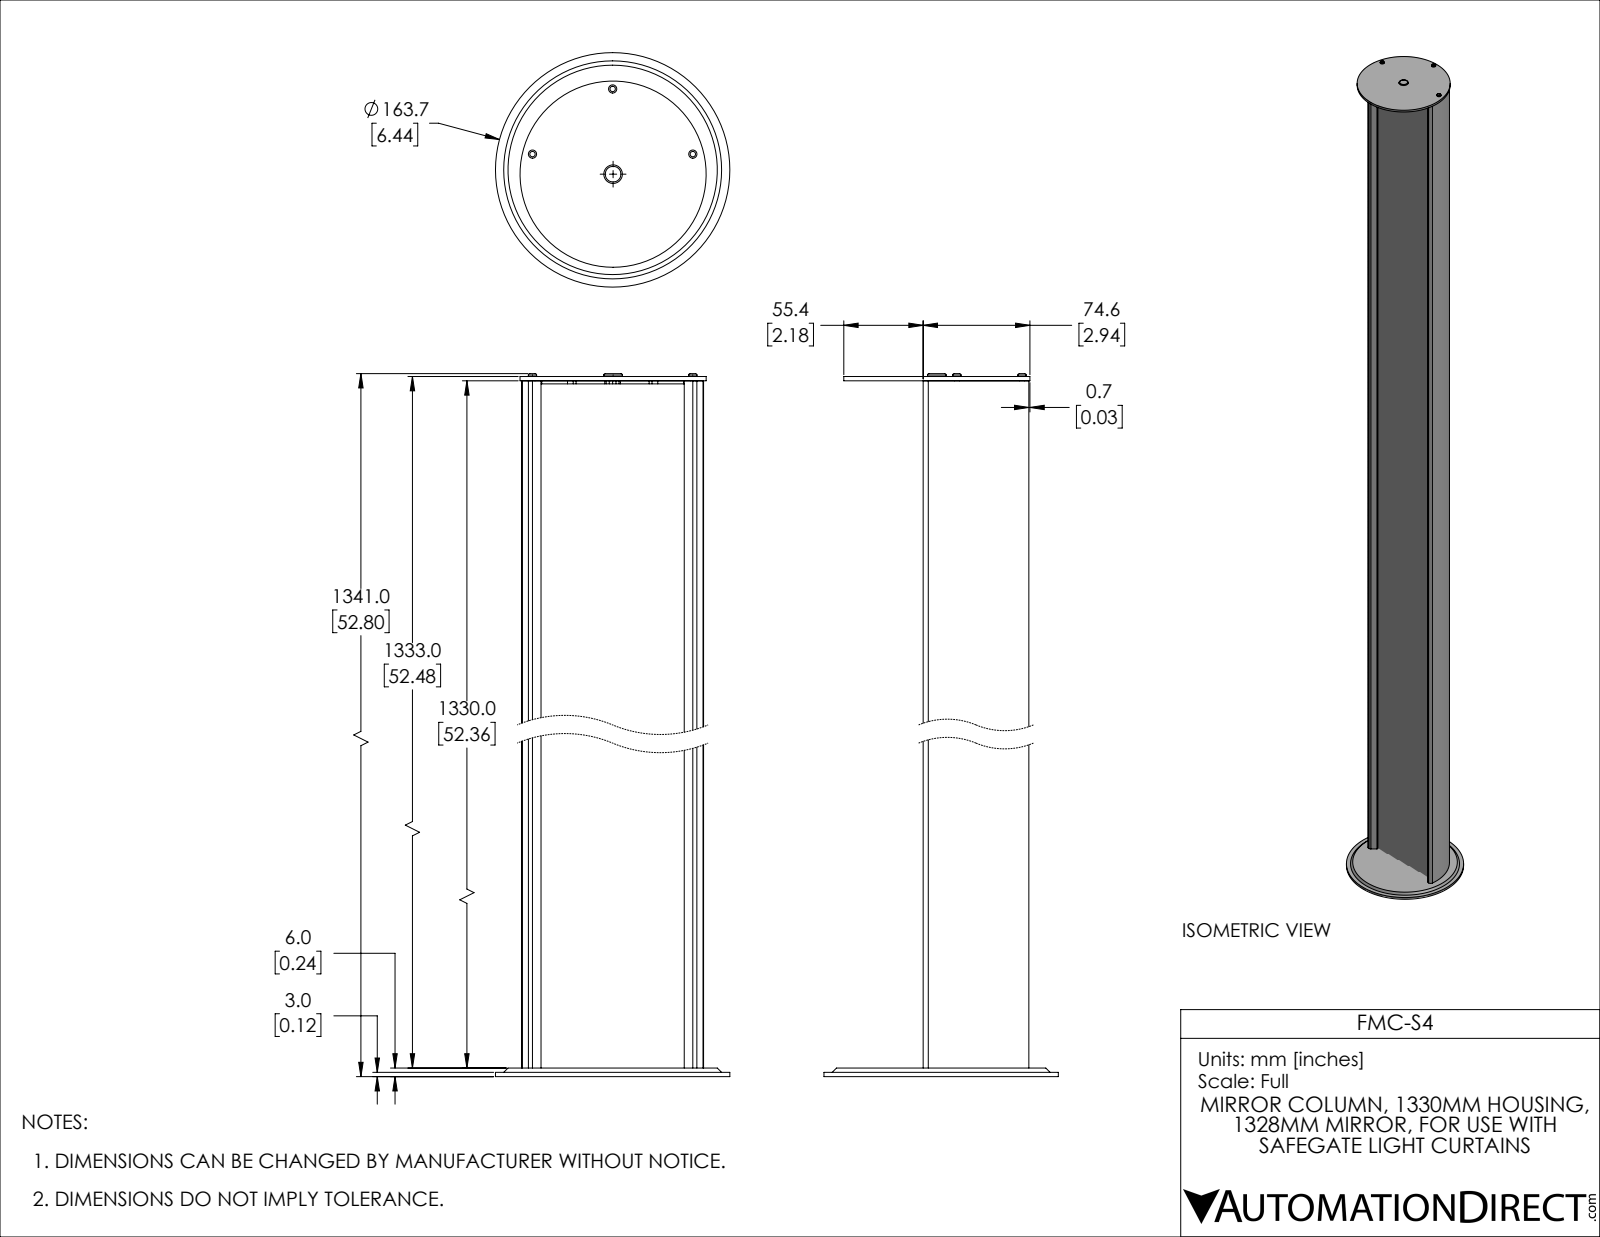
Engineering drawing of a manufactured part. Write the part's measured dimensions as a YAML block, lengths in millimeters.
part_name: "FMC-S4"
step_written_by: "SolidWorks 2019 (AUTOMOTIVE_DESIGN)"
units: millimeters
bodies: {solids: 11, faces: 192, planar: 82, cylindrical: 102, other: 8}
overall_size: [1341, 163.7, 163.7]
volume: 2411000
surface_area: 1668000
round_holes:
  - {diameter: 4, count: 3}
  - {diameter: 8.5, count: 3}
  - {diameter: 30, count: 1}
round_bosses_or_shafts:
  - {diameter: 6.3, count: 3}
  - {diameter: 5.8, count: 3}
  - {diameter: 3.5, count: 3}
  - {diameter: 163.7, count: 1}
  - {diameter: 130, count: 1}
  - {diameter: 13, count: 1}
partial_cylinders:
  - {radius: 0.5, count: 26}
  - {radius: 1, count: 7}
  - {radius: 2, count: 5}
  - {radius: 5.5, count: 4}
  - {radius: 2.7, count: 3}
  - {radius: 0.2, count: 2}
  - {radius: 1.5, count: 2}
  - {radius: 1.8, count: 2}
face_to_face_distances: [7.5, 1, 46.2, 53.7, 45.2, 52.7, 56, 56, 43, 42]
hole_center_spacings: [58.6, 72.2, 28.2, 112]
